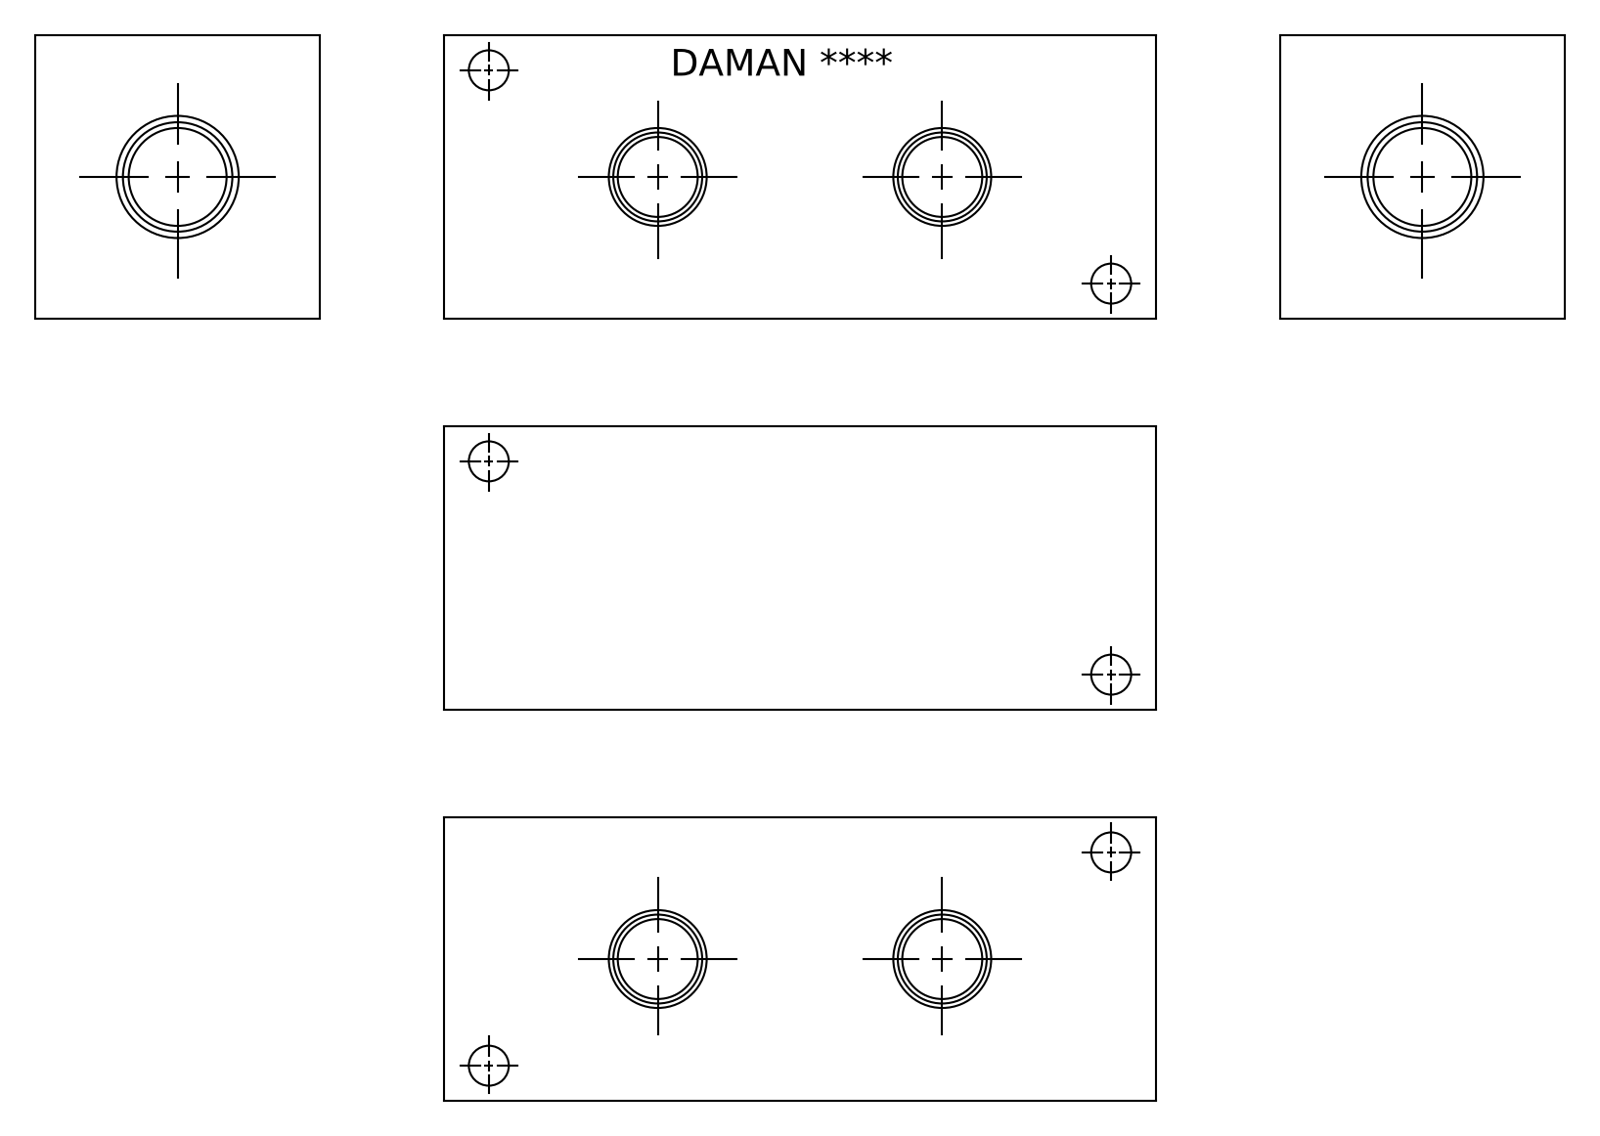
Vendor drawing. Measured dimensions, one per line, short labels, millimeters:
name: Part_AH1800206P.C13763R0_3D
written by: Autodesk Inventor 2019 (AUTOMOTIVE_DESIGN)
unit: mm
bodies: 1 solid, 350 faces (222 planar, 20 cylindrical, 108 other)
size: 127 × 50.8 × 50.8
volume: 295 502 mm³; area: 40 161 mm²
holes: 4× ⌀7.14, 2× ⌀14.3, 2× ⌀17.3, 1× ⌀17.48, 1× ⌀21.59
face distances: 50.8, 127, 11.73, 39.07, 15.37, 111.63, 27.34, 96.26, 49.8, 38.07
hole spacings: 35.69, 83.19, 117.51, 50.8
